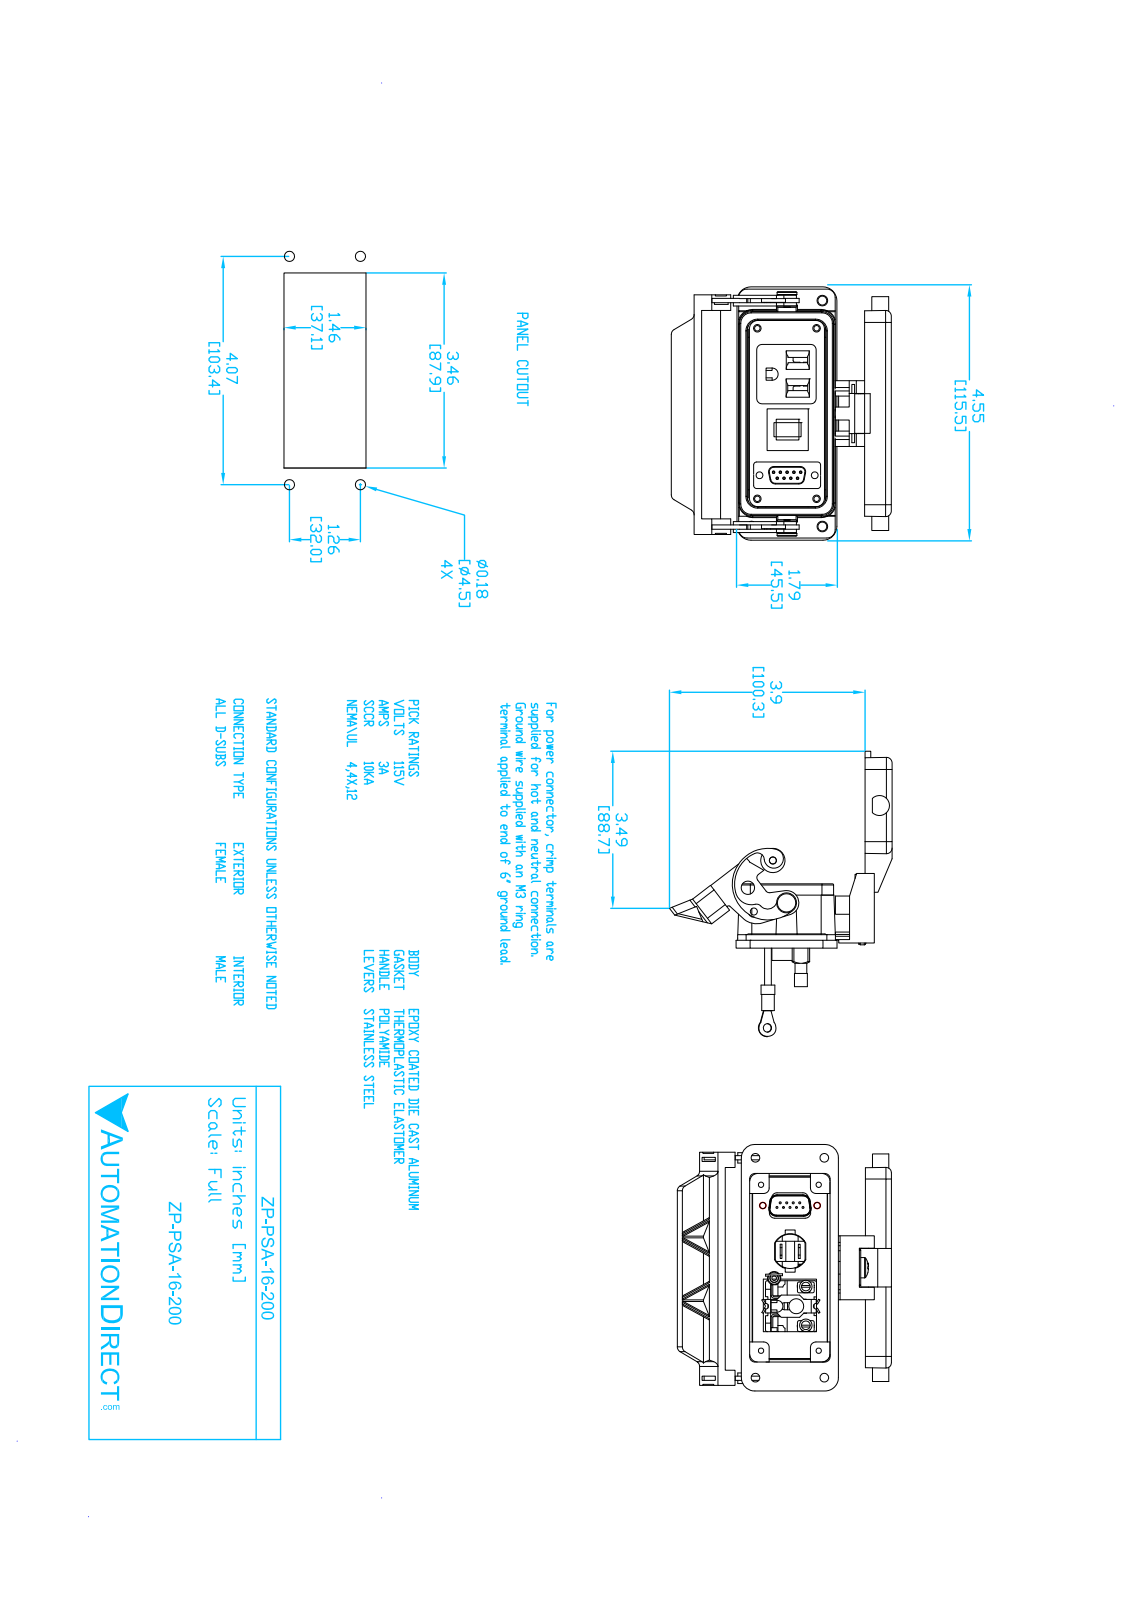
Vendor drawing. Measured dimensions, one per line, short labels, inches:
name: ZP-PSA-16-200
written by: SolidWorks 2017 (AUTOMOTIVE_DESIGN)
unit: in
bodies: 1 solid, 2081 faces (1122 planar, 499 cylindrical, 460 other)
size: 4.935 × 4.547 × 3.968
volume: 6.488 in³; area: 109.3 in²
holes: 6× ⌀0.16, 5× ⌀0.045, 4× ⌀0.045, 4× ⌀0.098, 4× ⌀0.144, 4× ⌀0.19, 2× ⌀0.09, 2× ⌀0.12, 2× ⌀0.122, 2× ⌀0.13, 2× ⌀0.134, 2× ⌀0.15
bosses: 9× ⌀0.038, 4× ⌀0.22, 4× ⌀0.118, 2× ⌀0.23, 2× ⌀0.21, 2× ⌀0.175, 2× ⌀0.109, 2× ⌀0.1
rounds: 16× R0.1, 13× R0.15, 12× R0.031, 10× R0.02, 9× R0.013, 9× R0.015, 8× R0.005, 8× R0.025
face distances: 0.672, 0.135, 0.115, 1.604, 0.02, 0.048, 0.72, 4.067, 1.543, 0.061
hole spacings: 0.12, 0.125, 0.24, 0.502, 1.261, 3.564, 3.748, 0.214
